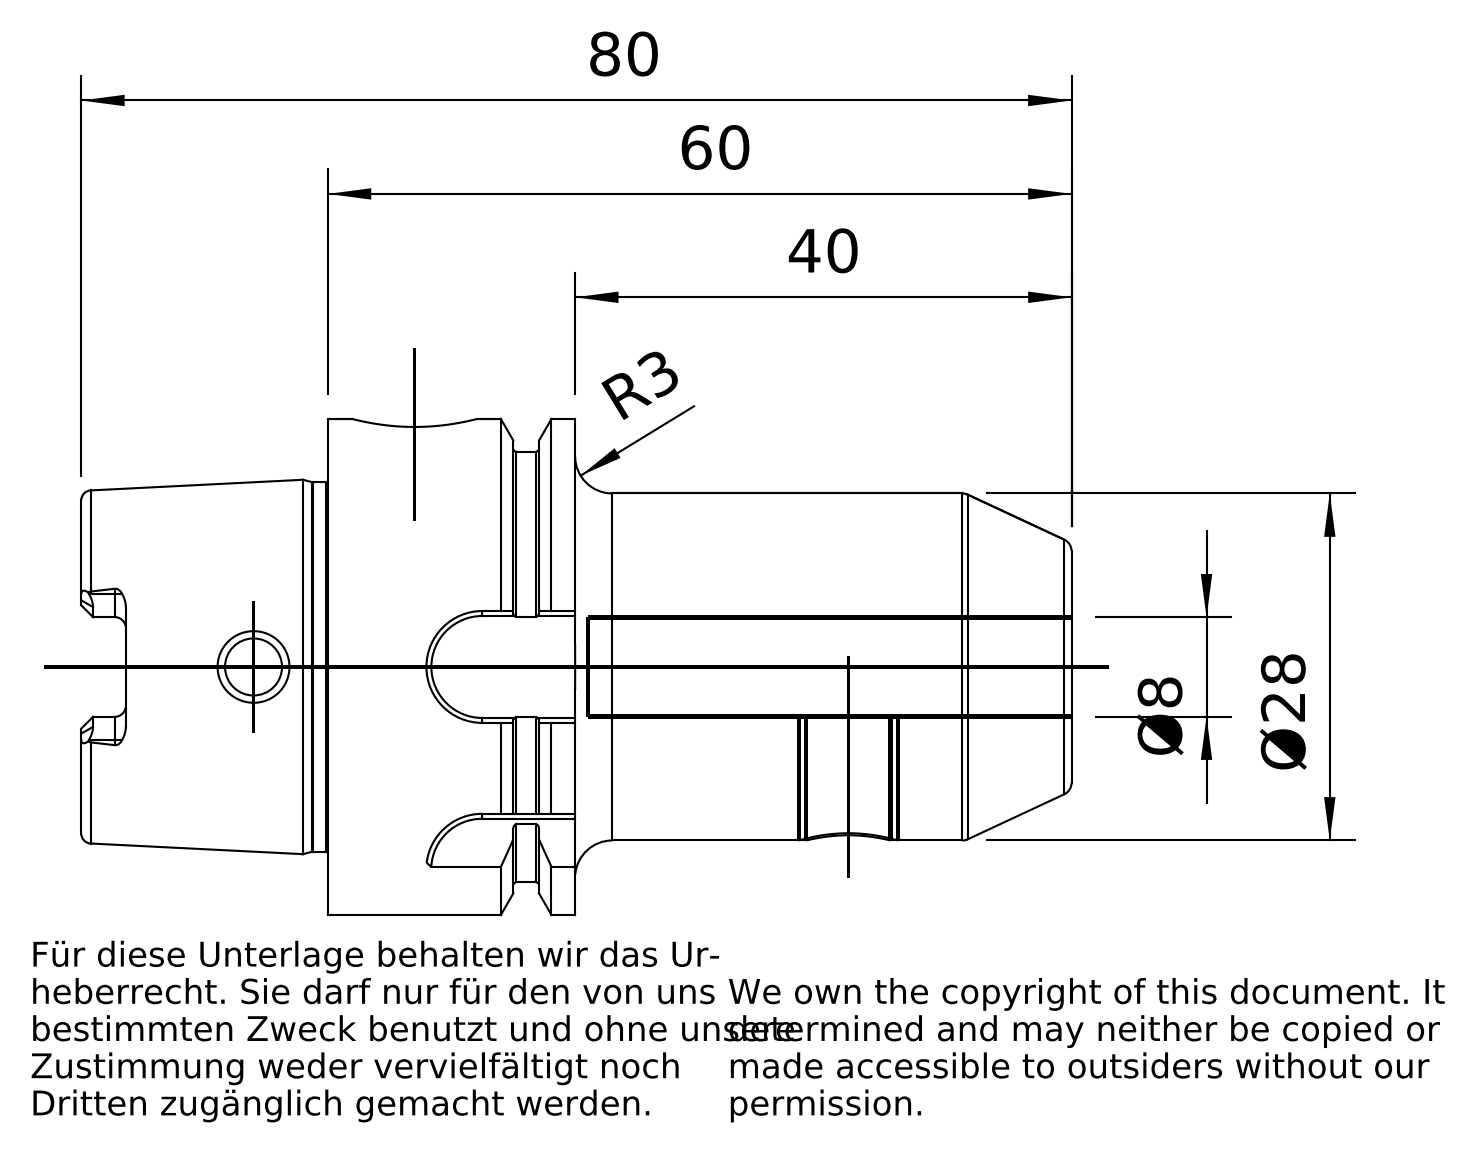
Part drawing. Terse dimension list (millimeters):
name: A40-000-08
written by: PRO/ENGINEER BY PARAMETRIC TECHNOLOGY CORPORATION, 2010430 (CONFIG_CONTROL_DESIGN)
unit: mm
bodies: 1 solid, 193 faces (63 planar, 54 cylindrical, 76 other)
size: 79.9 × 40 × 40
volume: 45 220 mm³; area: 14 207 mm²
holes: 2× ⌀8, 1× ⌀4.6, 1× ⌀6.8, 1× ⌀10, 1× ⌀10.2, 1× ⌀12, 1× ⌀12.22, 1× ⌀12.5, 1× ⌀21.04, 1× ⌀25.57
bosses: 1× ⌀40, 1× ⌀34.75, 1× ⌀29.81, 1× ⌀28
rounds: 6× R0.9, 4× R1.88, 3× R4.5, 1× R4.51
face distances: 19.95, 60, 40.05, 7.95, 12, 52.05, 19.9, 27.85, 39.85, 79.9
hole spacings: 35
